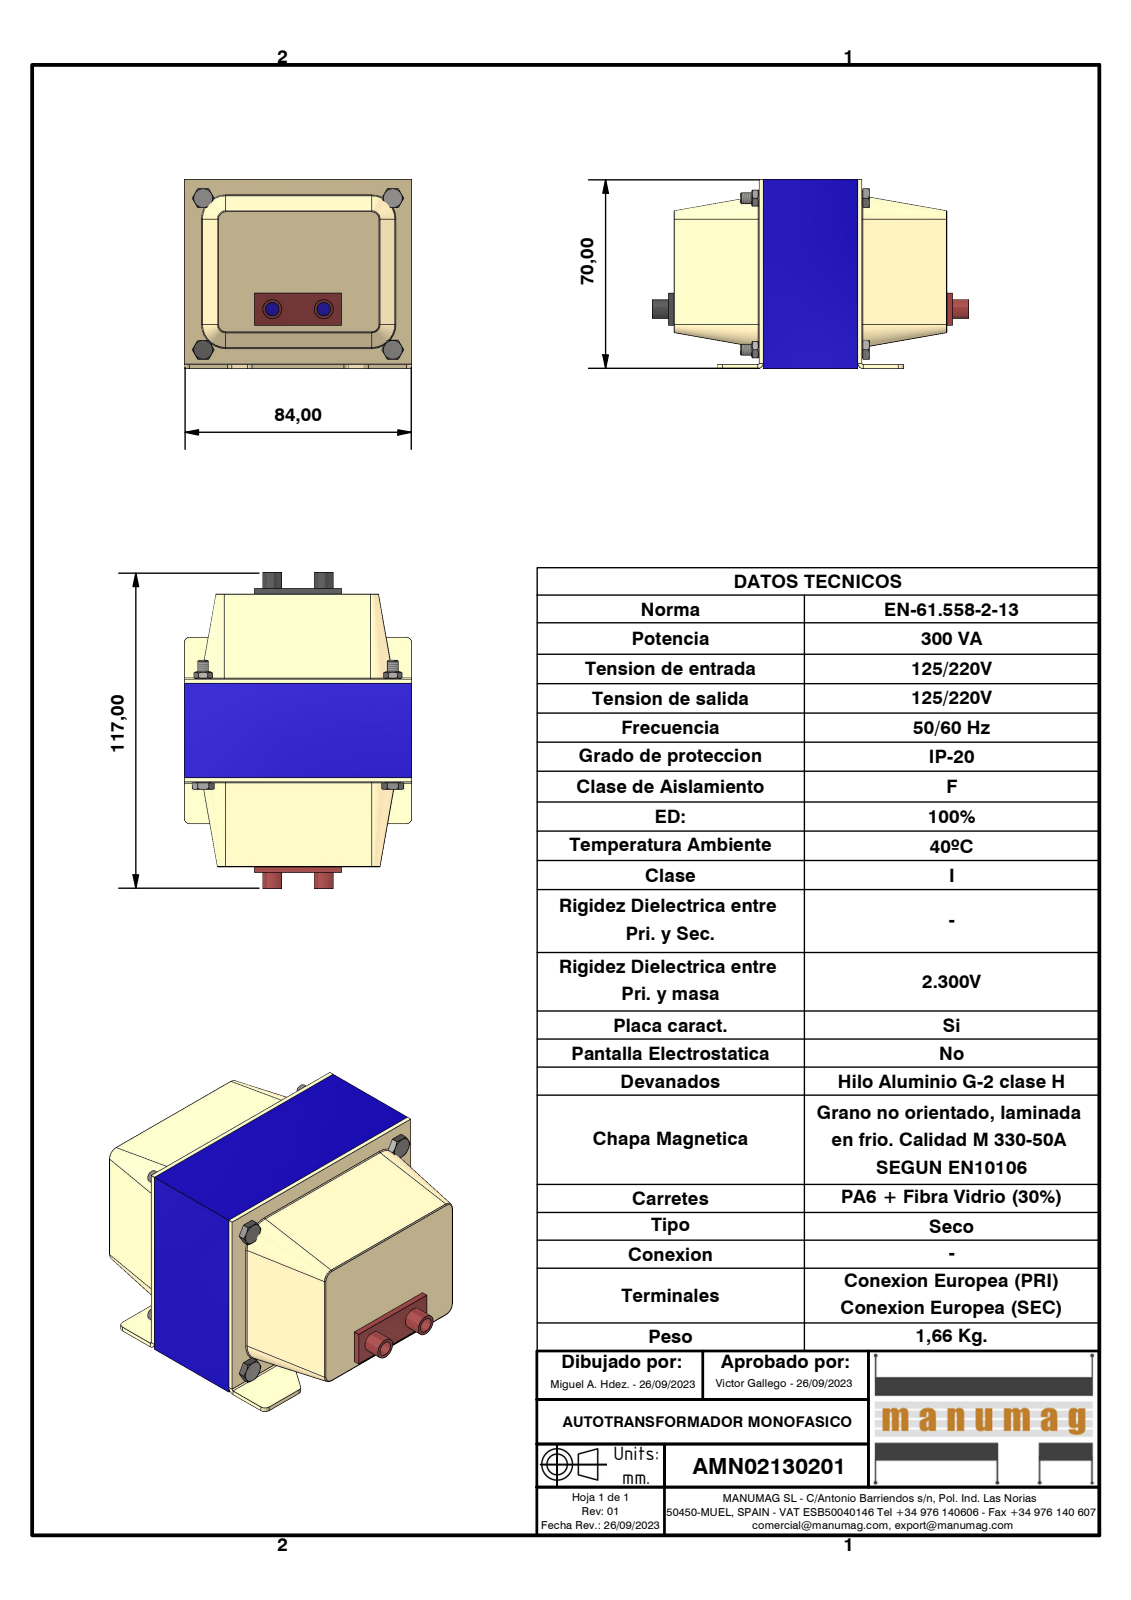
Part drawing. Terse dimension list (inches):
name: AMN02130201; EI84 x 70 - 35 (RC28) Azul; TAPA RC28 RECEPTACULO; Receptaculo Rojo (+3 more)
written by: Autodesk Inventor 2023 (AUTOMOTIVE_DESIGN)
unit: in
bodies: 13 solids, 310 faces (162 planar, 68 cylindrical, 80 other)
size: 4.606 × 3.307 × 2.756
volume: 11.35 in³; area: 133.1 in²
holes: 8× ⌀0.157, 4× ⌀0.112, 4× ⌀0.177, 2× ⌀0.197
bosses: 4× ⌀0.232, 4× ⌀0.143, 2× ⌀0.276
rounds: 16× R0.015, 14× R0.079, 2× R0.02
face distances: 0.059, 2.677, 1.24, 0.551, 1.378, 2.427, 2.756, 2.205, 1.299, 1.102
hole spacings: 2.756, 3.529, 1.849, 2.205, 1.165, 1.165, 1.9, 1.901
